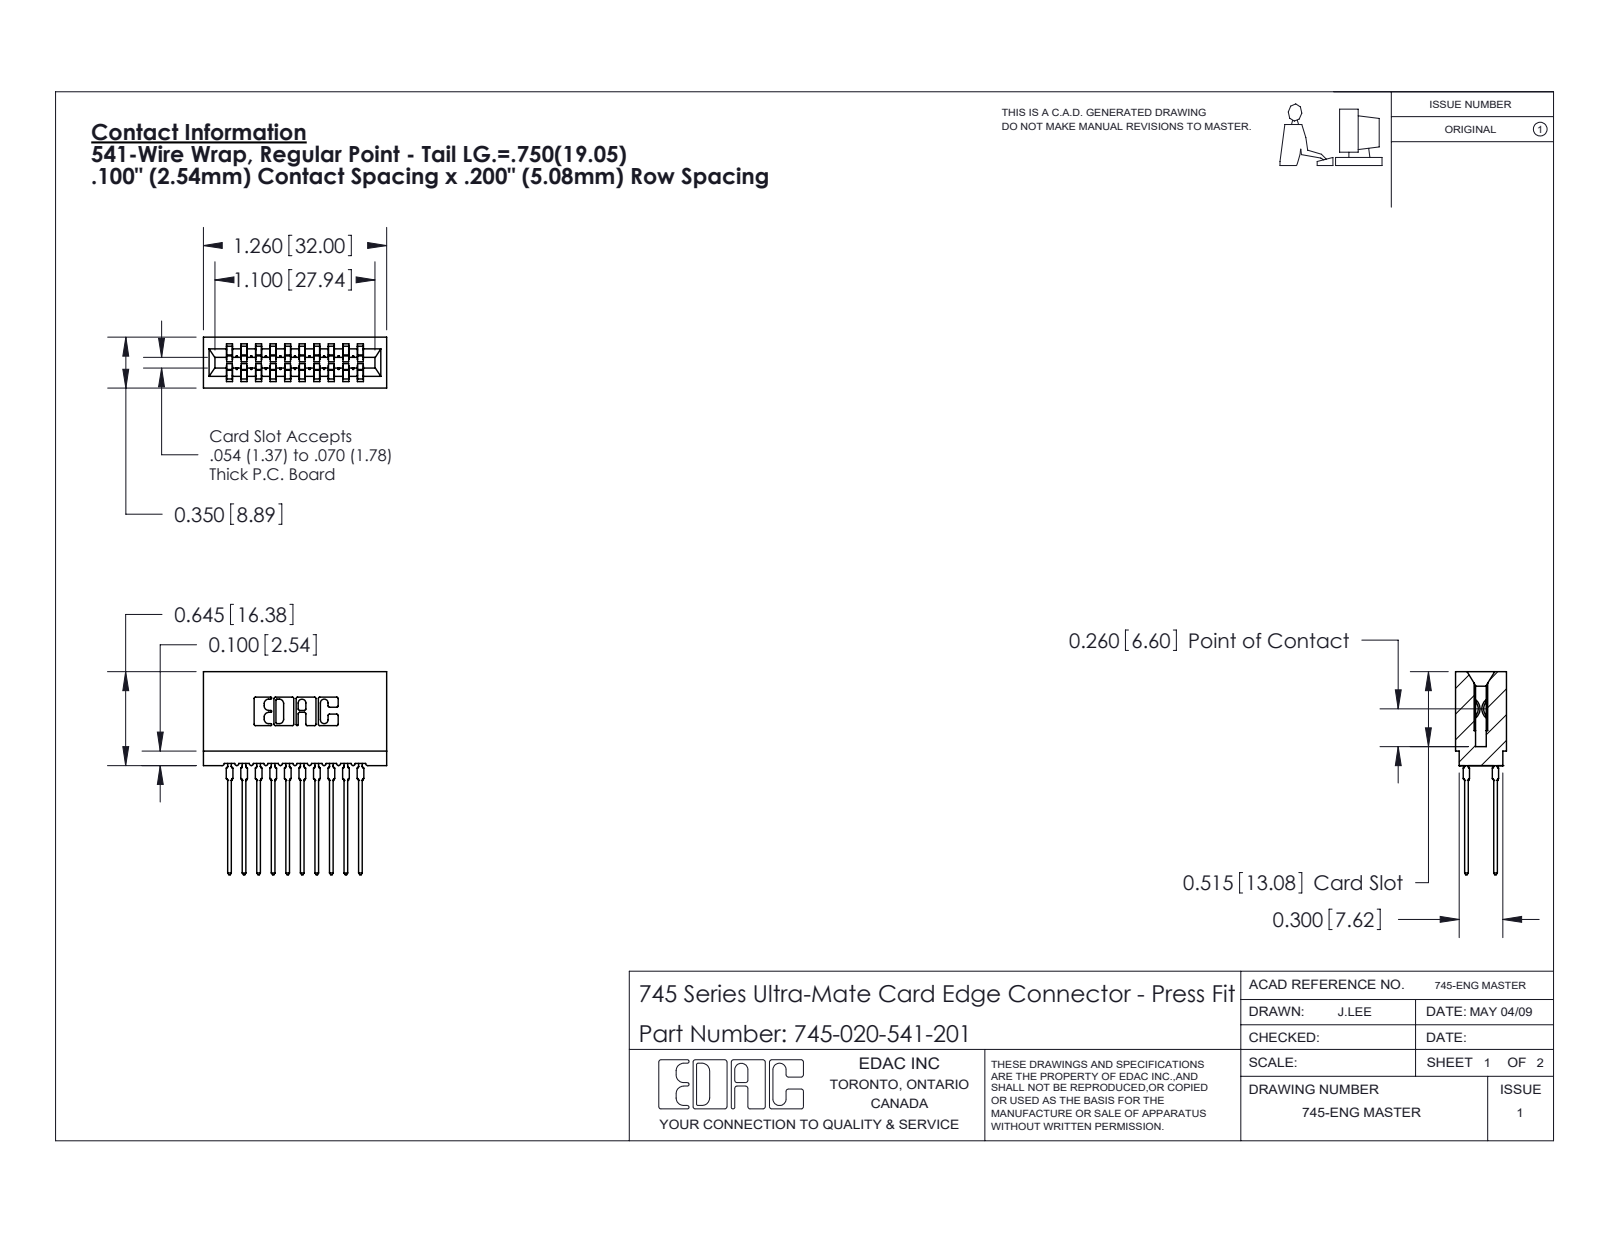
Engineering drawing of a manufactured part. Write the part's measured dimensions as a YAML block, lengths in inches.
part_name: "745-292-001_541; 745-020-541-201; 745 Part_Insulator Option - 01"
step_written_by: "SolidWorks 2020 (CONFIG_CONTROL_DESIGN)"
units: inches
bodies: {solids: 21, faces: 1885, planar: 975, cylindrical: 390, other: 520}
overall_size: [1.396, 1.26, 0.35]
volume: 0.194
surface_area: 9.468
partial_cylinders:
  - {radius: 0.021, count: 40}
  - {radius: 0.01, count: 22}
  - {radius: 0.015, count: 20}
  - {radius: 0.005, count: 8}
  - {radius: 0.011, count: 8}
  - {radius: 0.007, count: 6}
  - {radius: 0.031, count: 6}
  - {radius: 0.026, count: 3}
face_to_face_distances: [0.2, 0.1, 0.3, 0.4, 0.5, 0.158, 0.058, 0.042, 0.258, 0.142]
